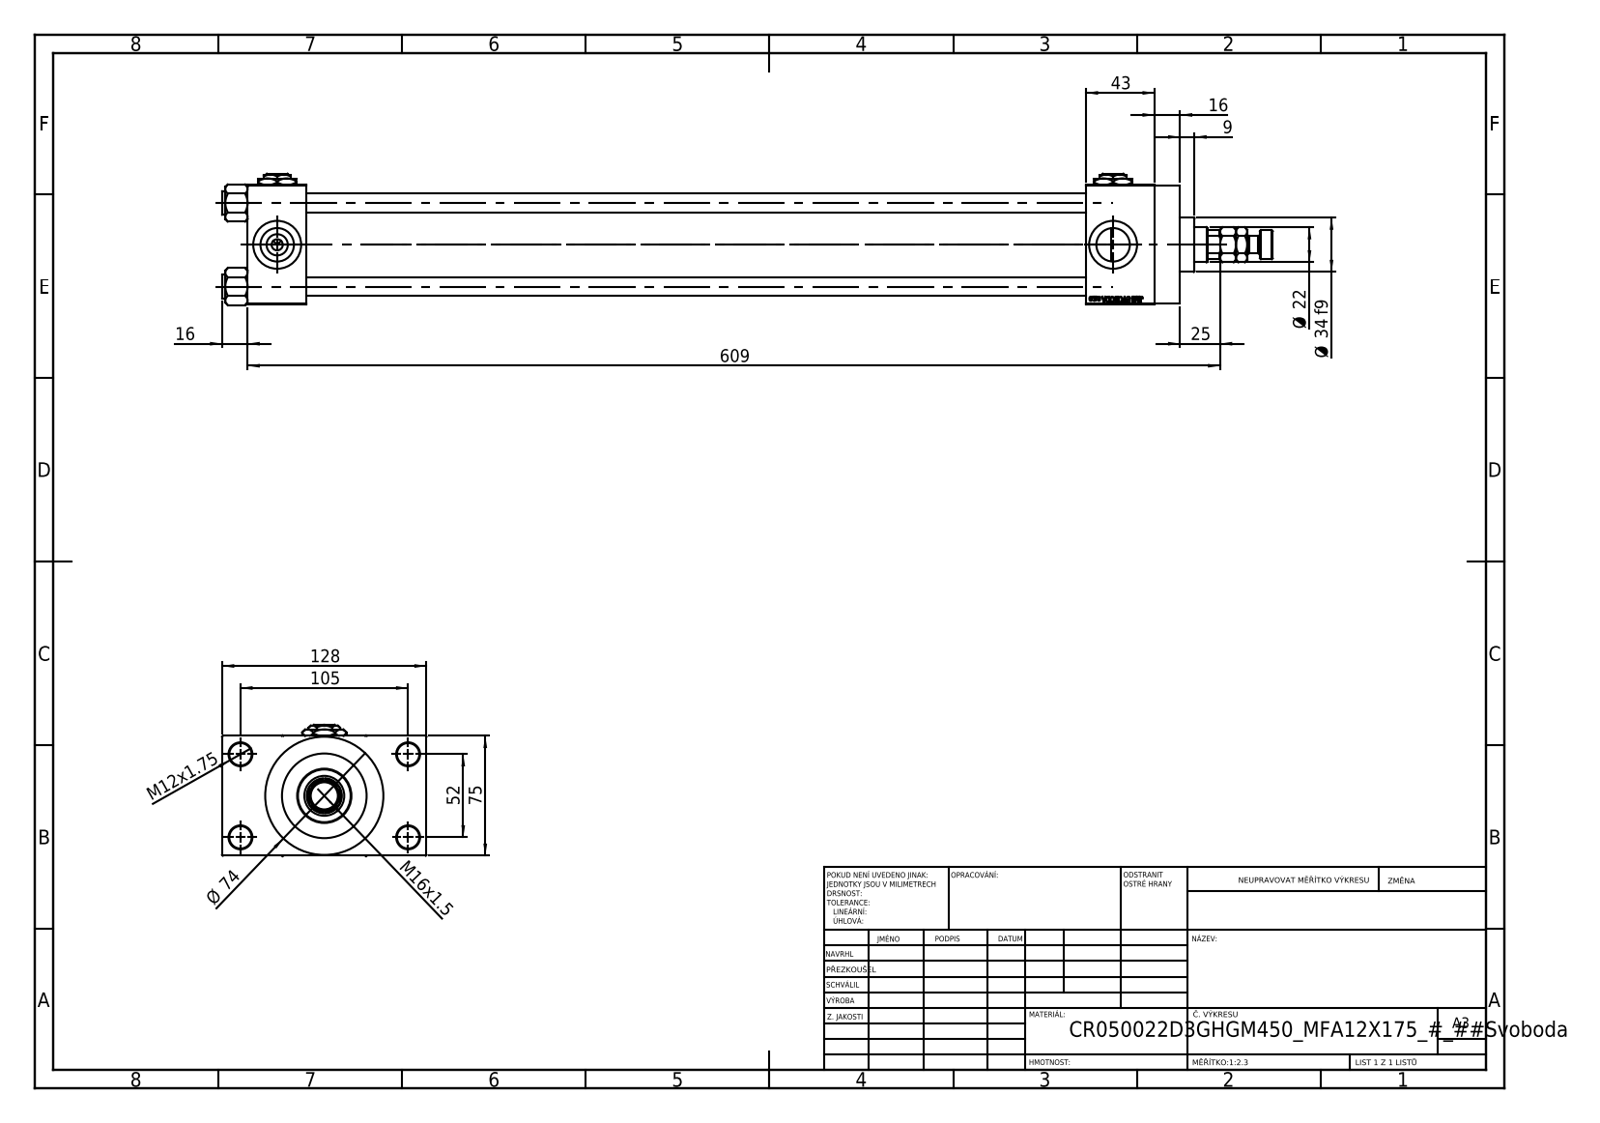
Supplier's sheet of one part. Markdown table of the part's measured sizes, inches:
| quantity | value |
| --- | --- |
| part name | V215CR_VCP_D; V215CR_D_Body; V215_VC_A; NUT_M5_D (+3 more) |
| STEP written by | SolidWorks 2019 (CONFIG_CONTROL_DESIGN) |
| units | inches |
| bodies | 14 solids, 1256 faces (561 planar, 103 cylindrical, 592 other) |
| overall size | 25.906 × 5.039 × 3.239 |
| volume | 83.85 in³ |
| surface area | 637.6 in² |
| round holes (diameter × count) | 0.472 × 4, 0.551 × 4, 0.825 × 4, 1.181 × 4, 0.276 × 3, 0.413 × 1, 0.866 × 1, 0.984 × 1, 1.614 × 1, 1.969 × 1, 2.087 × 1 |
| round bosses / shafts (diameter × count) | 0.591 × 4, 2.913 × 1, 2.205 × 1, 1.339 × 1, 0.709 × 1, 0.433 × 1 |
| partial cylindrical surfaces (radius × count) | 0.413 × 1 |
| main face-to-face distances | 2.953, 19.213, 1.457, 20.669, 1.043, 22.362, 20.906, 1.693, 3.996, 0.63 |
| hole center spacings | 1.037, 1.456, 2.059, 2.3, 2.307, 3.096, 3.715, 2.047 |
